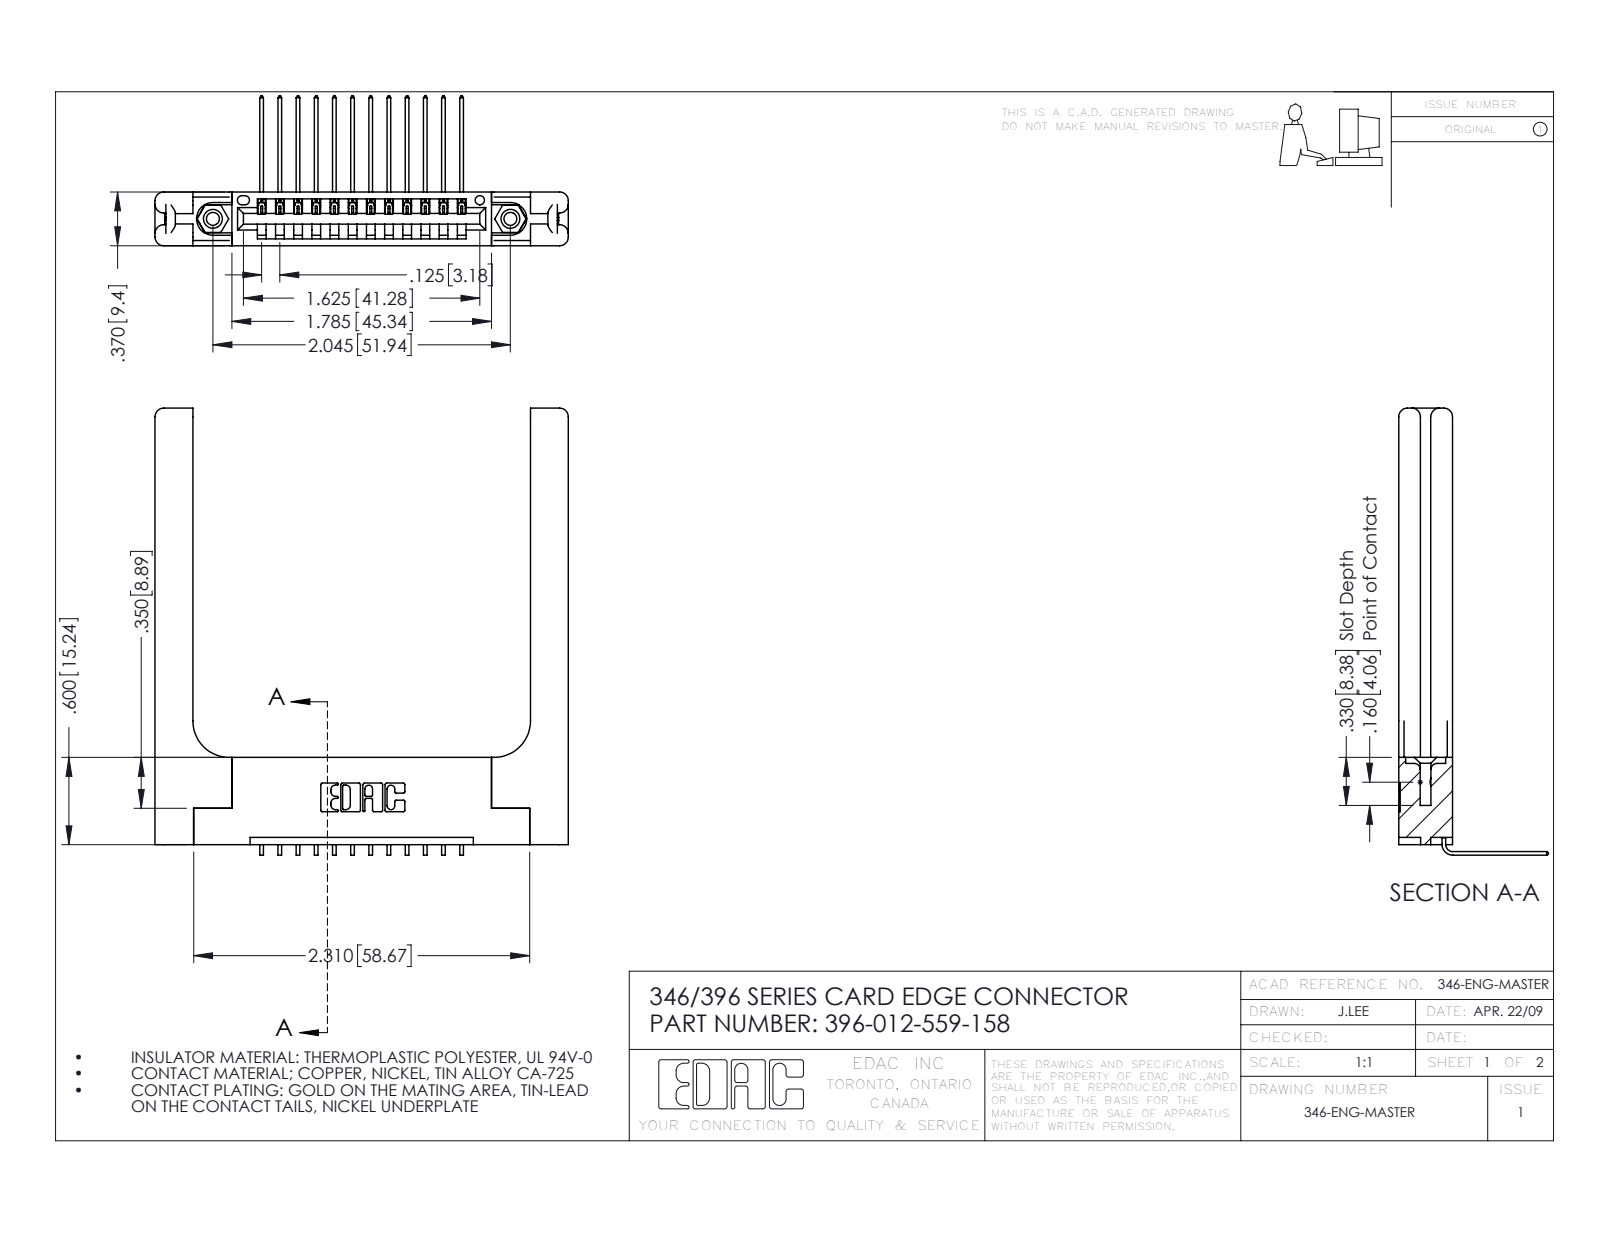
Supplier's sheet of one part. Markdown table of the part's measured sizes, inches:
| quantity | value |
| --- | --- |
| part name | 345-292-001_558 559 Tail - 1; 345-250-001_345-250-001-102; 346 Part_Flush Mounting Lugs - 0.156 Dia-TH; 346-220-058_345-220-058 (+1 more) |
| STEP written by | SolidWorks 2016 (CONFIG_CONTROL_DESIGN) |
| units | inches |
| bodies | 17 solids, 1098 faces (728 planar, 310 cylindrical, 60 other) |
| overall size | 3.073 × 2.841 × 1.03 |
| volume | 0.87 in³ |
| surface area | 20.94 in² |
| round holes (diameter × count) | 0.089 × 2, 0.125 × 2, 0.156 × 2, 0.064 × 1 |
| round bosses / shafts (diameter × count) | 0.155 × 2 |
| partial cylindrical surfaces (radius × count) | 0.006 × 24, 0.01 × 22, 0.06 × 16, 0.007 × 6, 0.031 × 6, 0.026 × 3, 0.03 × 2, 0.031 × 2 |
| main face-to-face distances | 0.37, 0.15, 0.072, 0.322, 0.048, 0.148, 0.22, 0.25, 0.102, 0.173 |
| hole center spacings | 0.246, 1.839, 2.045 |
